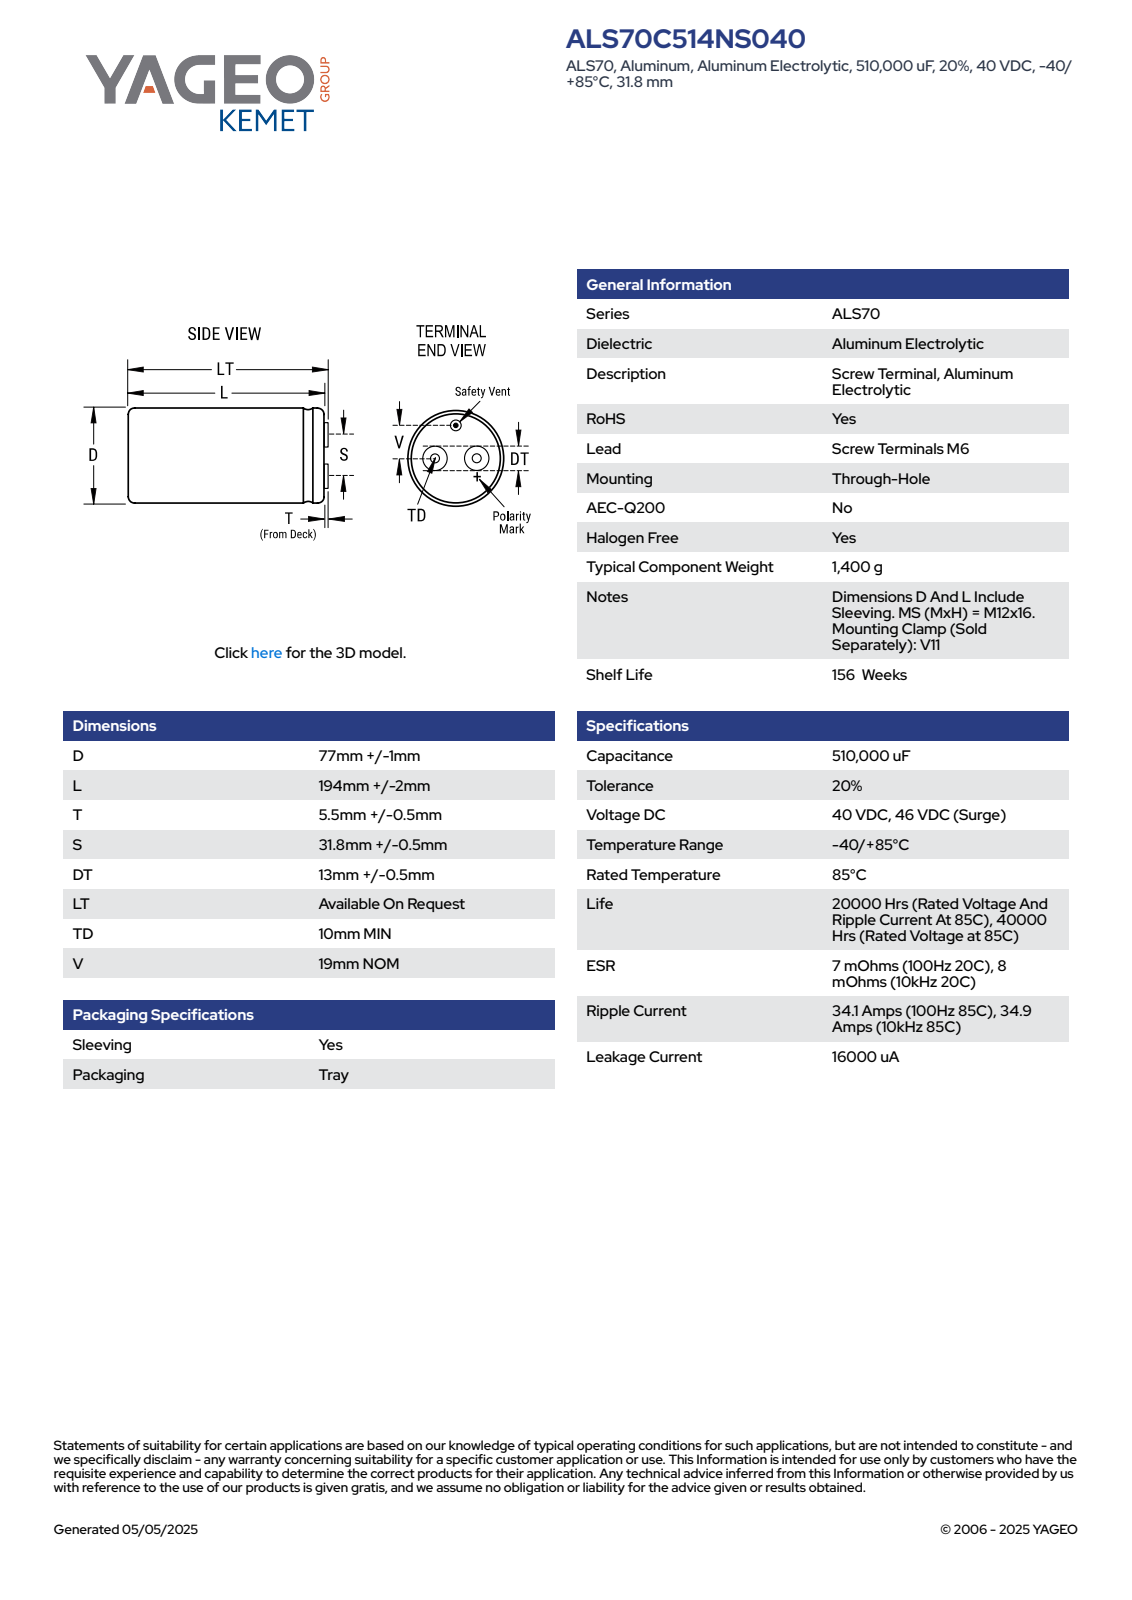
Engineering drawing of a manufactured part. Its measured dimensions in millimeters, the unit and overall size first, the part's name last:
Units: millimetres
Overall size (bounding box): 202 × 78.01 × 78
Round holes (diameter × count): ⌀5 ×2, ⌀1.33 ×1
Round bosses / shafts (diameter × count): ⌀13.5 ×2, ⌀78 ×1, ⌀2.27 ×1
Partial cylindrical surfaces — rounded edges, fillets, slot ends (radius × count): R39.01 ×1
Main face-to-face distances: 196, 202, 6, 192, 4, 10, 196.35, 4.35, 0.35, 5.65
Hole centre spacings: 24.78, 31.8
Volume: 930 470 mm³ · Surface area: 58 397 mm²
Bodies: 1 solid, 88 faces (30 planar, 19 cylindrical, 39 other)
Part name (STEP PRODUCT): CARC_KAR_77X194_D78L196T6S31.8DT13.500TD10.000V19.000
STEP written by: SolidWorks 2014 (AUTOMOTIVE_DESIGN)
